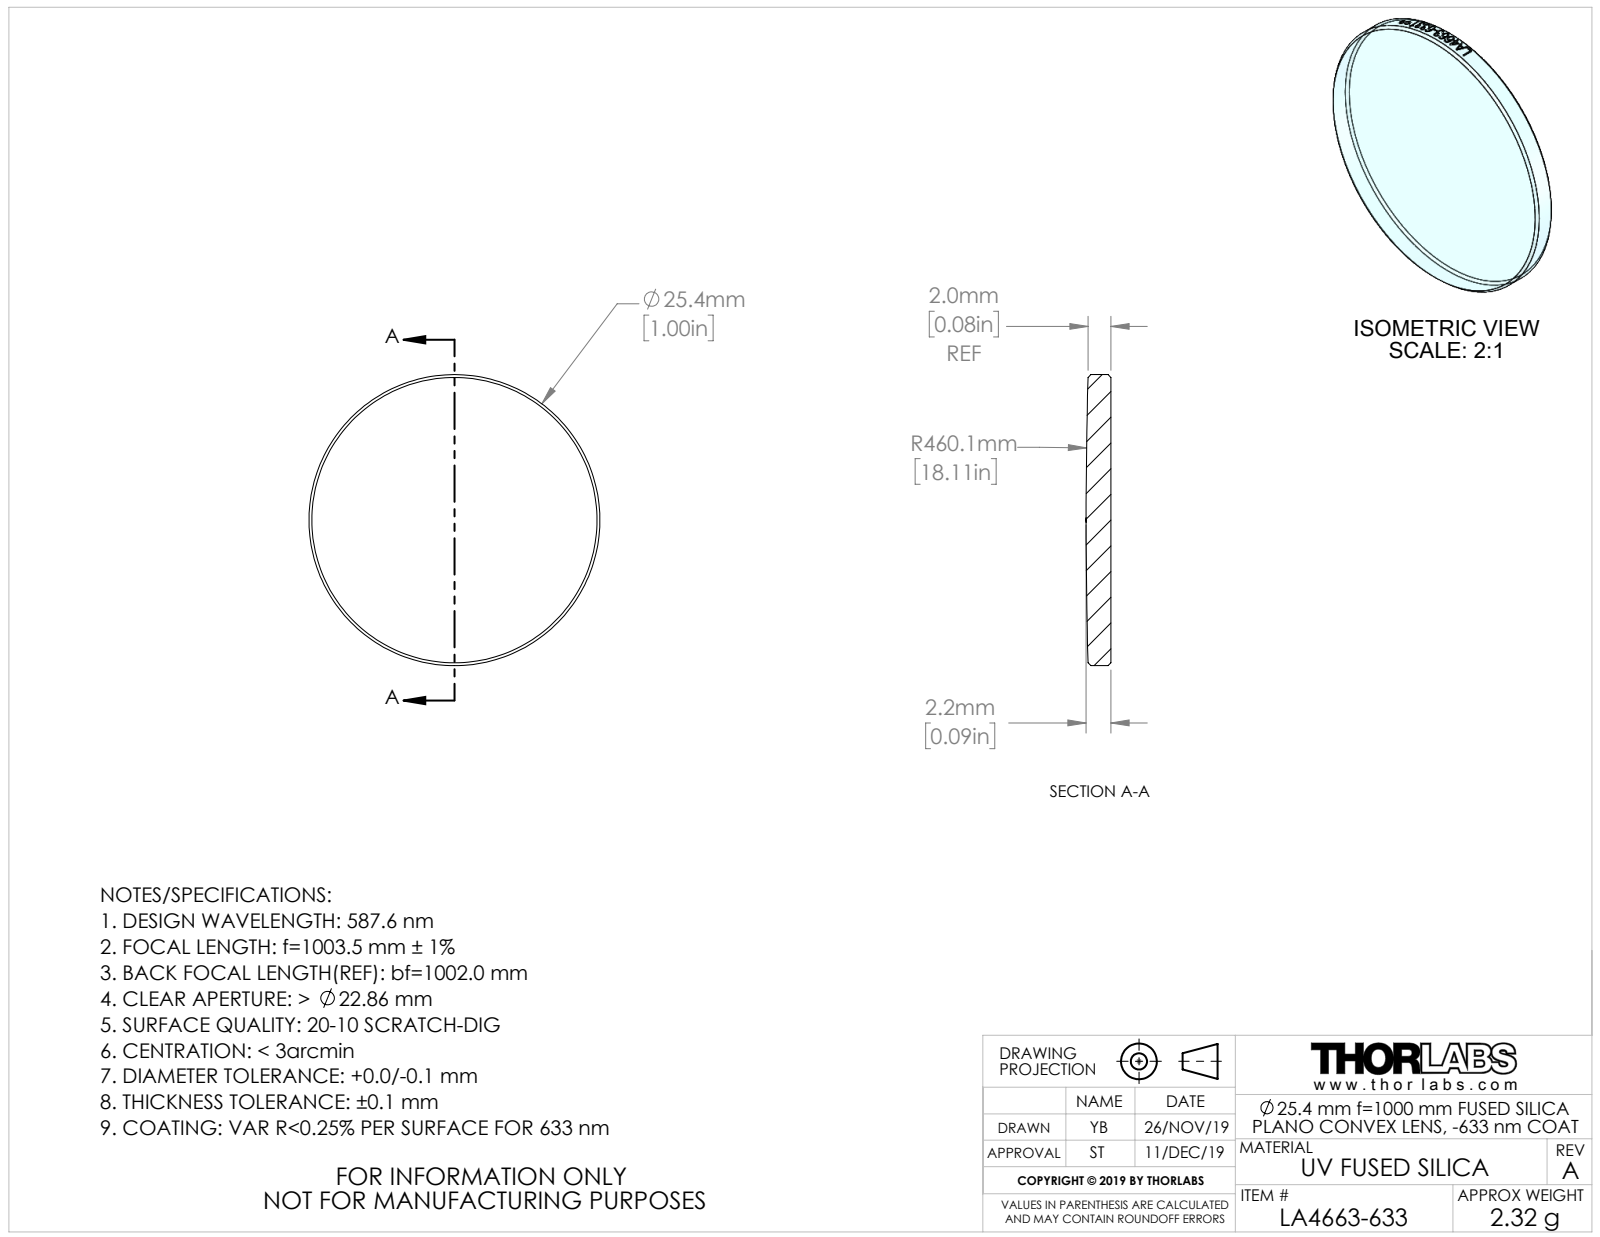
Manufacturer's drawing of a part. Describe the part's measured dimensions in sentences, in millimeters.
The part is named "CTN015007; CTN014988-999". Its 3-D file was written by "SolidWorks 2018 (AUTOMOTIVE_DESIGN)". It is 1 solid with 32 faces: 1 planar, 25 cylindrical and 6 other. Overall it measures 25.4 by 25.4 by 2.17 millimeters. Its volume is 1 052 cubic millimeters and its surface area 1 150 square millimeters. Round bosses or shafts: 1 of diameter 25.4.
